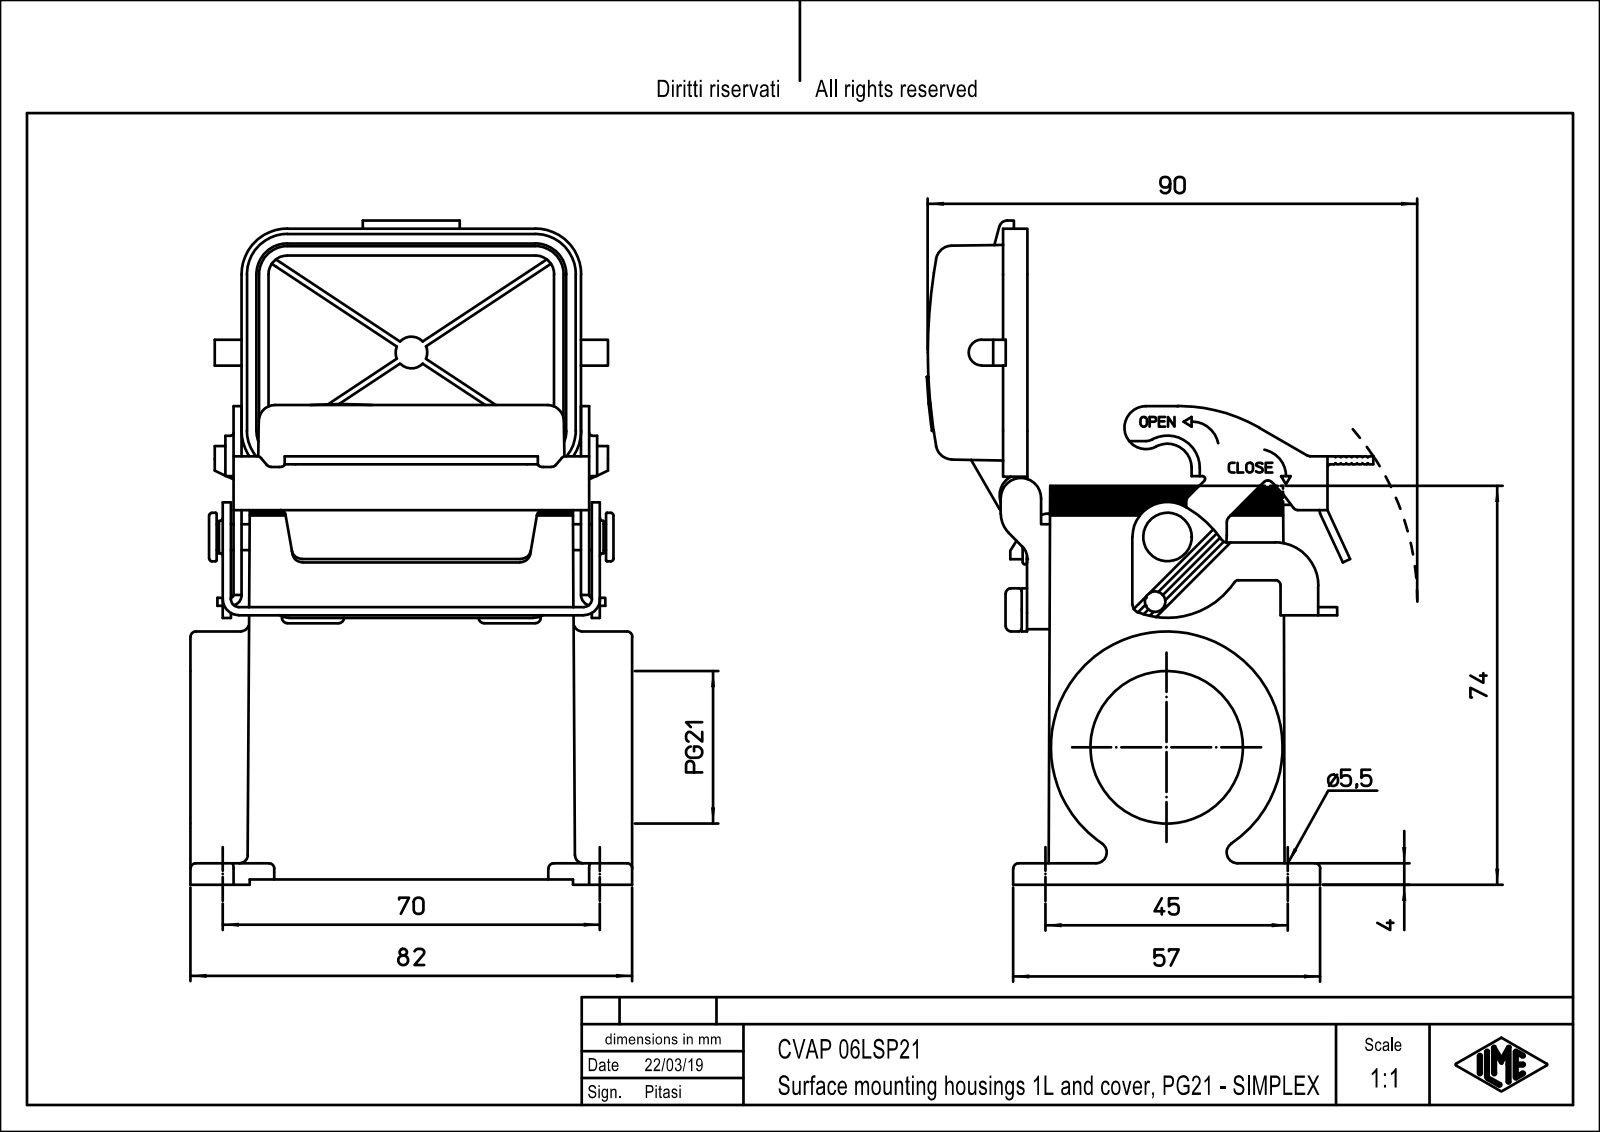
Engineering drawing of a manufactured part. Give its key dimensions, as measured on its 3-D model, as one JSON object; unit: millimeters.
{"part_name": "CVAP_06_LSP21", "step_written_by": "Creo Elements/Direct Modeling 18.1F 24-Jul-2014 (C) Parametric Technology GmbH (AUTOMOTIVE_DESIGN)", "units": "millimeters", "bodies": {"solids": 1, "faces": 649, "planar": 352, "cylindrical": 261, "other": 36}, "overall_size": [122.72, 82, 80.58], "volume_mm3": 108367, "surface_area_mm2": 62496, "round_holes": [[2.46, 4], [3, 4], [5.5, 4], [24.4, 1], [26.8, 1]], "round_bosses_or_shafts": [[0.8, 3], [9, 1], [8, 1], [5, 1], [2.4, 1]], "partial_cylinders_radius": [[0.25, 16], [0.33, 15], [1, 15], [0.5, 12], [1.5, 12], [2, 10], [1.4, 6], [2.8, 6]], "face_to_face_distances": [4, 40.5, 1.4, 44.5, 36.5, 2, 6.75, 58.5, 10.75, 47.75], "hole_center_spacings": [15.81, 38.28, 57.71, 67.42, 27, 44, 45, 51.62]}
